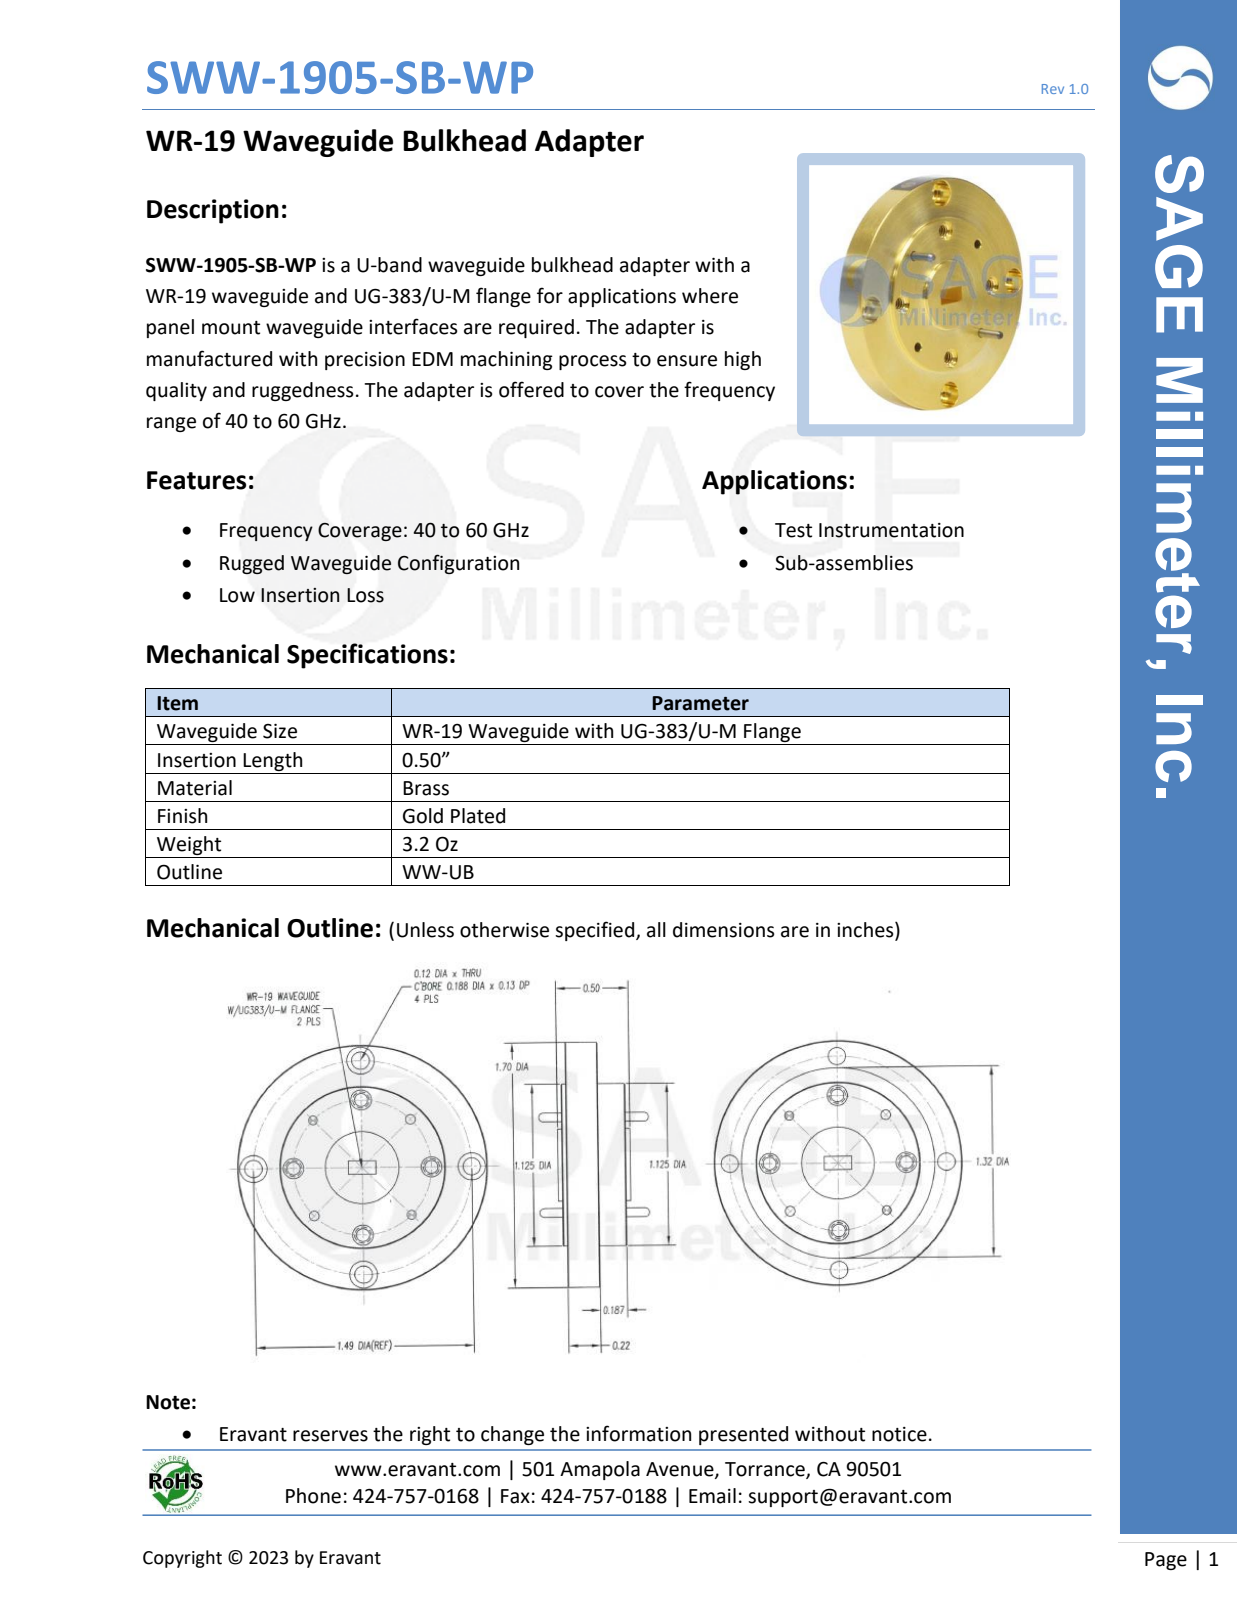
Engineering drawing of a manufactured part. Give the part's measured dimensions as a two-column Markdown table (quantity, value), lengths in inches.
| quantity | value |
| --- | --- |
| part name | DMWW-19-105-B |
| STEP written by | SolidWorks 2013 (CONFIG_CONTROL_DESIGN) |
| units | inches |
| bodies | 5 solids, 187 faces (31 planar, 84 cylindrical, 72 other) |
| overall size | 1.7 × 1.7 × 0.715 |
| volume | 0.663 in³ |
| surface area | 8.74 in² |
| round holes (diameter × count) | 0.061 × 4, 0.067 × 4, 0.089 × 4, 0.12 × 4, 0.14 × 4, 0.187 × 4, 1.325 × 1 |
| round bosses / shafts (diameter × count) | 0.063 × 4, 1.7 × 1, 1.125 × 1, 0.5 × 1 |
| main face-to-face distances | 0.03, 0.44, 0.222, 0.41, 0.188, 0.252, 0.177, 0.147, 0.075, 0.263 |
| hole center spacings | 0.359, 0.528, 0.663, 0.866, 1.124, 0.469, 0.878, 0.743 |
